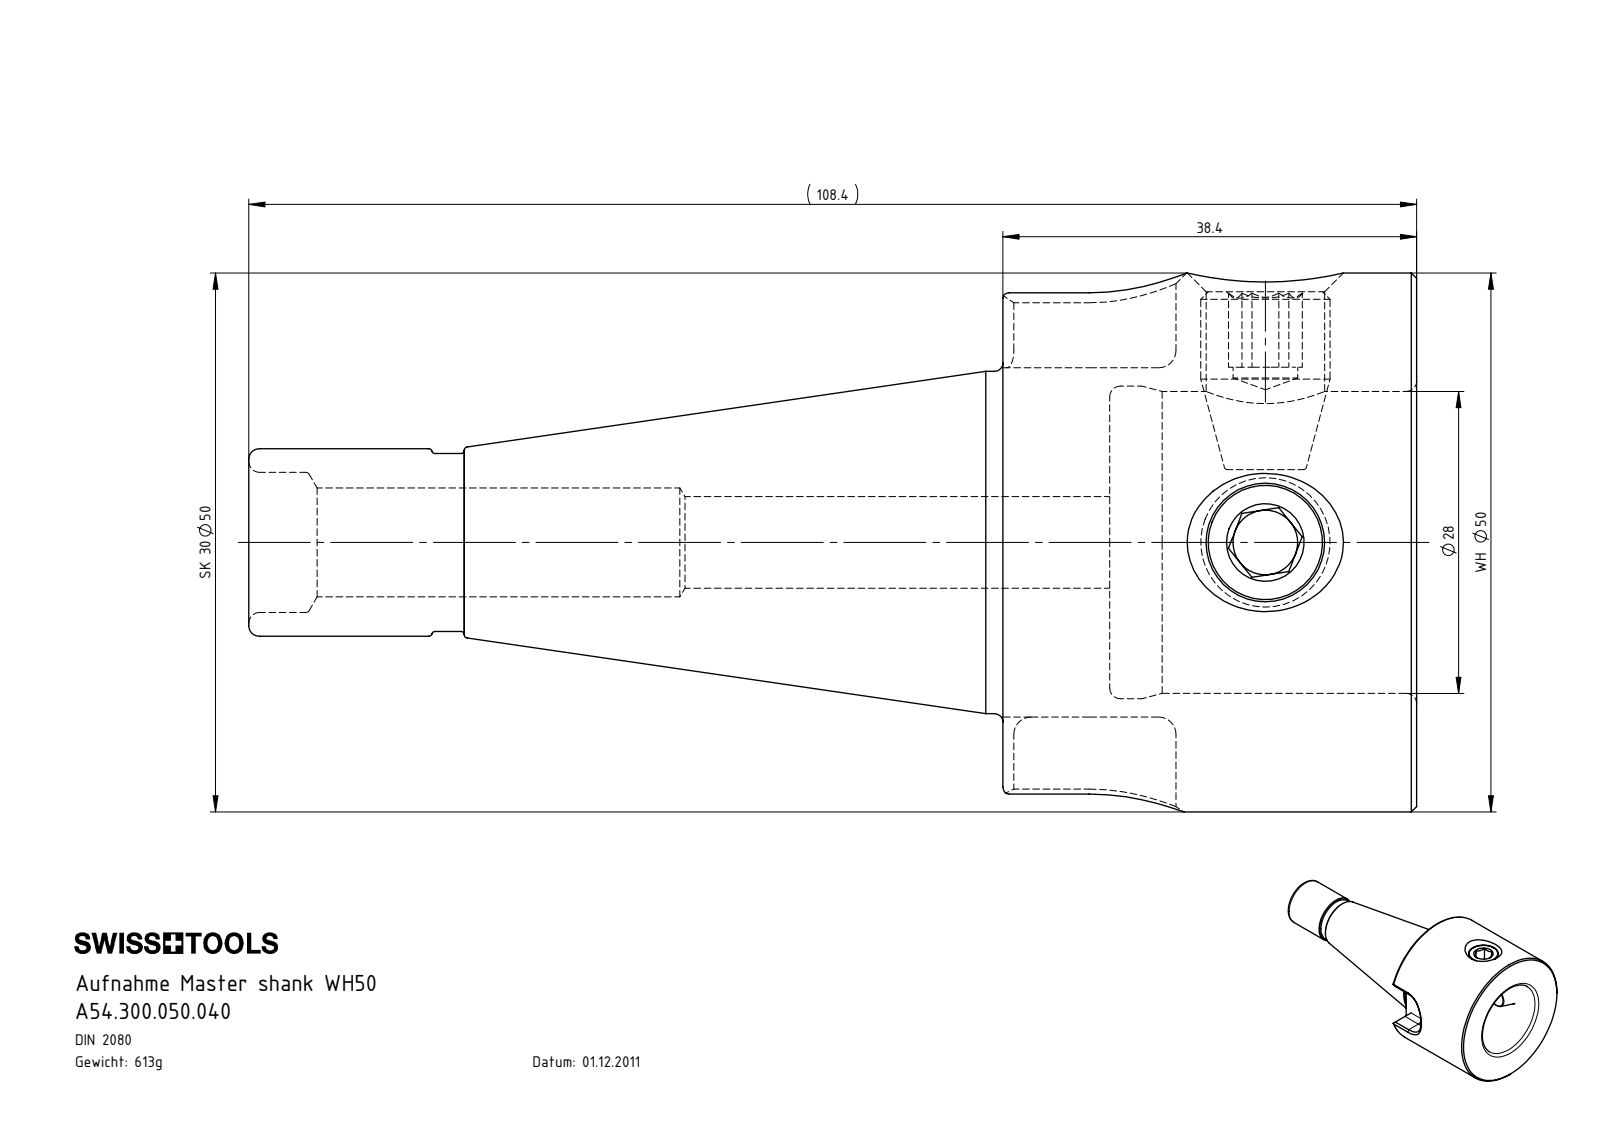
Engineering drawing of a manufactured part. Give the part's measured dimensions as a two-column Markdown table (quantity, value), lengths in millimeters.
| quantity | value |
| --- | --- |
| part name | WH5-ER1.001.017; SZ3-WH5.K01.040_B; A54.300.050.040 |
| STEP written by | SolidWorks 2022 (CONFIG_CONTROL_DESIGN) |
| units | millimeters |
| bodies | 3 solids, 151 faces (49 planar, 39 cylindrical, 63 other) |
| overall size | 108.4 × 50 × 50 |
| volume | 78 100 mm³ |
| surface area | 21 379 mm² |
| round holes (diameter × count) | 6 × 2, 11 × 2, 8.5 × 1, 10.1 × 1, 13 × 1, 28 × 1, 29 × 1 |
| round bosses / shafts (diameter × count) | 12 × 2, 50 × 1, 31.75 × 1, 17.4 × 1, 16.5 × 1 |
| partial cylindrical surfaces (radius × count) | 1.6 × 6, 8.05 × 1 |
| main face-to-face distances | 38.4, 9.9, 28.5, 32.4, 6, 16.5, 16.1, 31.3, 15.2, 7.05 |
